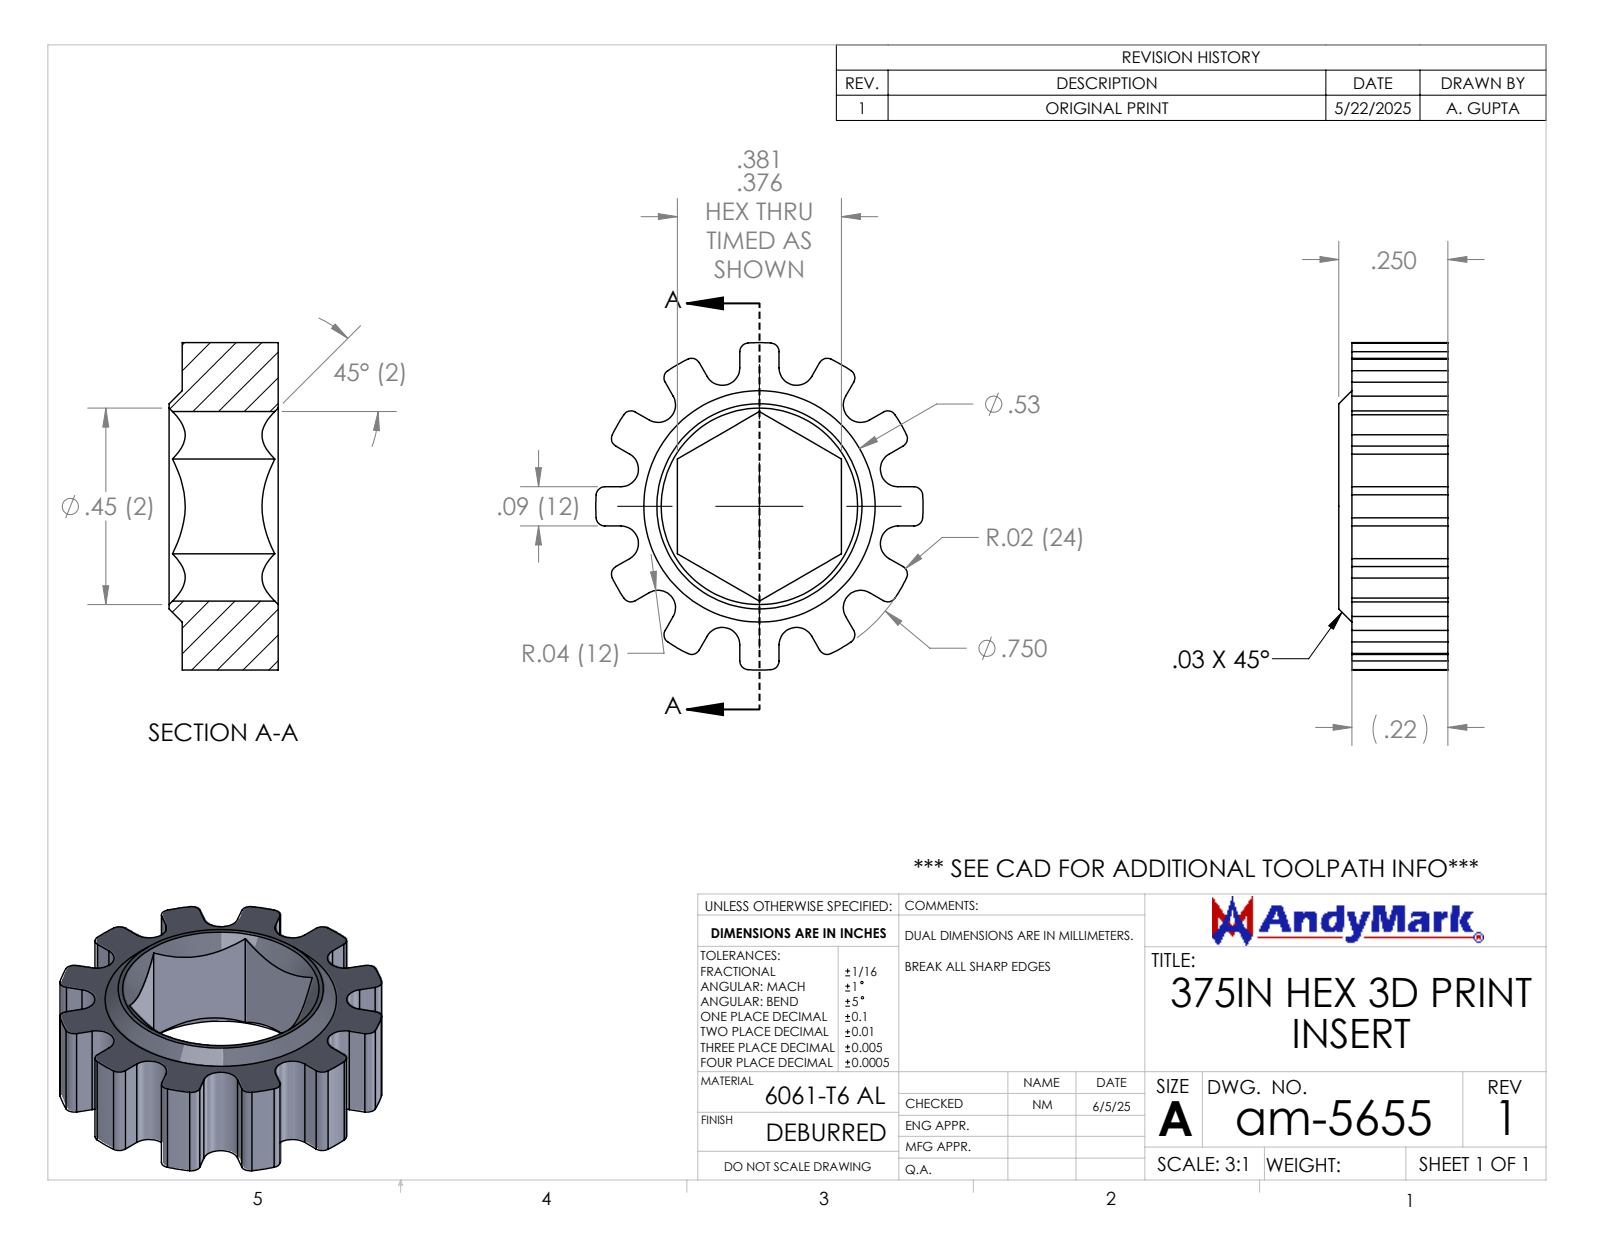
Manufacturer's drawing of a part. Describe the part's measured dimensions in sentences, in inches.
The part is named "am-5655 375in Hex 3D Print Insert". Its 3-D file was written by "SolidWorks 2024 (AUTOMOTIVE_DESIGN)". It is 1 solid with 96 faces: 33 planar, 57 cylindrical and 6 other. Overall it measures 0.75 by 0.75 by 0.25 inches. Its volume is 0.053 cubic inches and its surface area 1.546 square inches. Partial cylindrical surfaces (rounded edges, fillets, slot ends): 24 of radius 0.02, 12 of radius 0.04, 1 of radius 0.375. The main face-to-face distances are 0.22, 0.376, 0.143, 0.233, 0.09, 0.25, 0.03.
